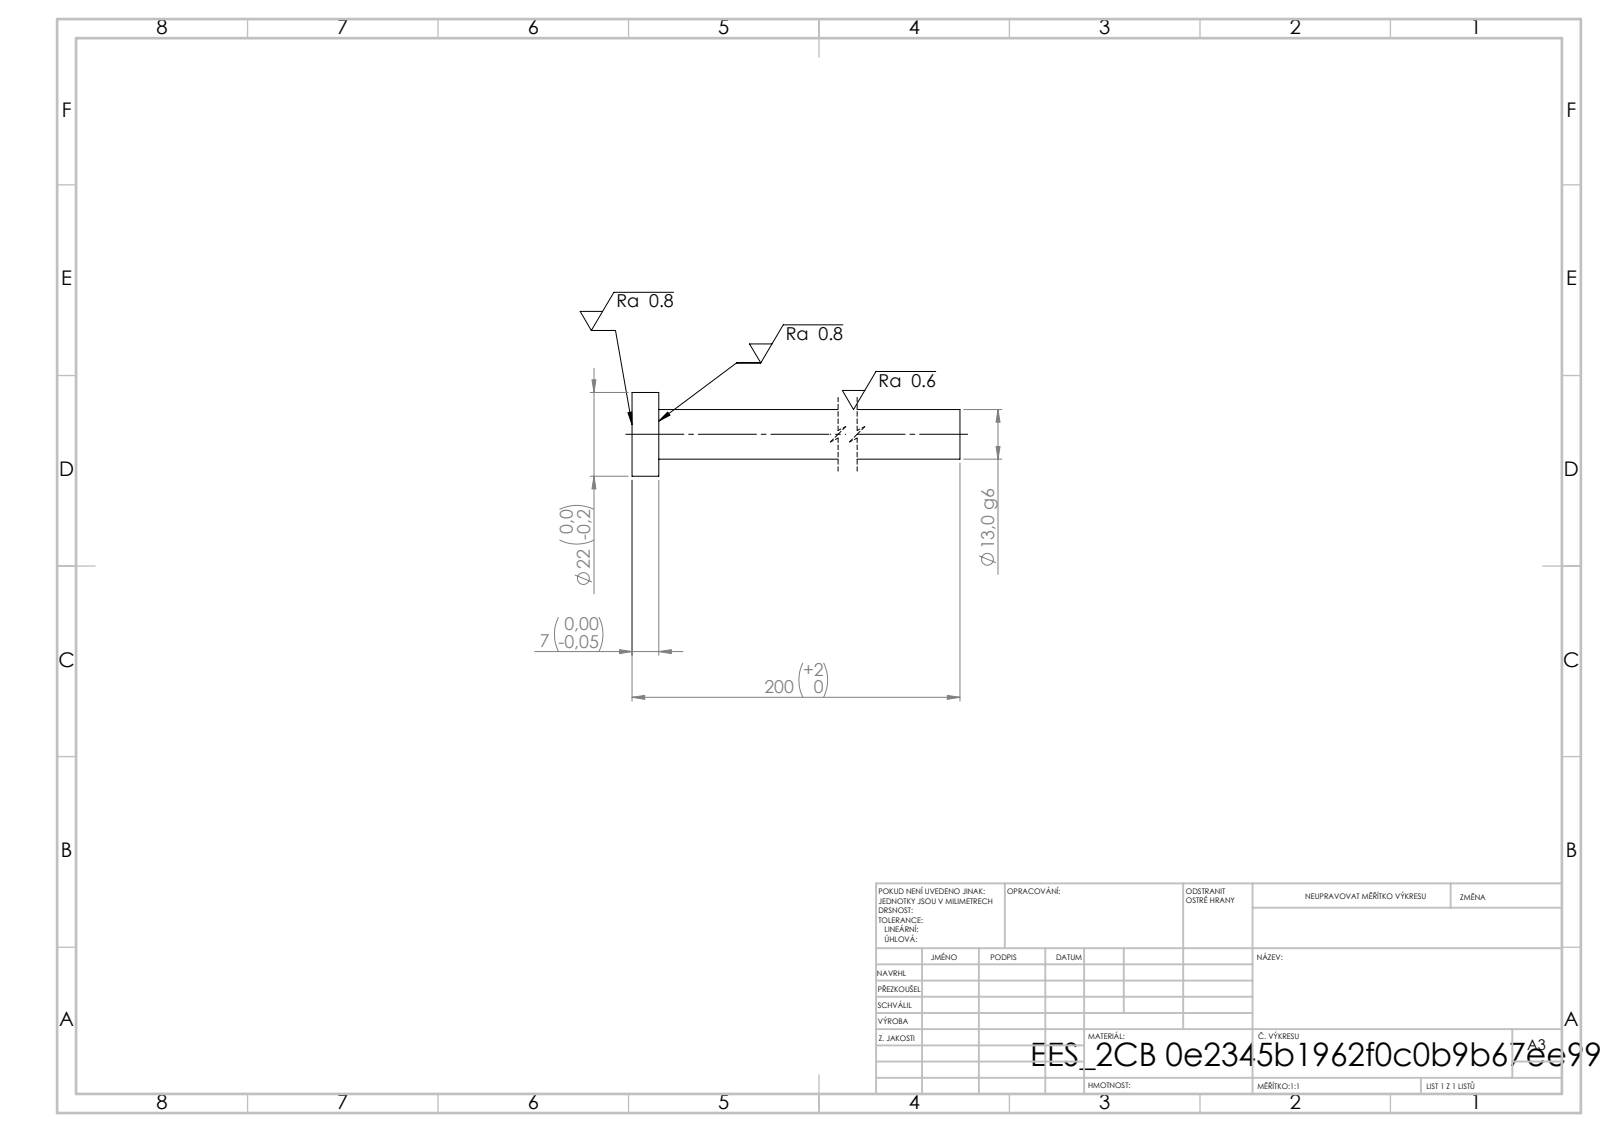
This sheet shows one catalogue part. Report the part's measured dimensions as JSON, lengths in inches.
{"step_written_by": "SolidWorks 2019 (CONFIG_CONTROL_DESIGN)", "units": "inches", "bodies": {"solids": 1, "faces": 7, "planar": 3, "cylindrical": 4, "other": 0}, "overall_size": [7.874, 0.866, 0.866], "volume_in3": 1.726, "surface_area_in2": 14.15, "round_bosses_or_shafts": [[0.866, 1], [0.512, 1]], "face_to_face_distances": [0.276, 7.874, 7.598]}
